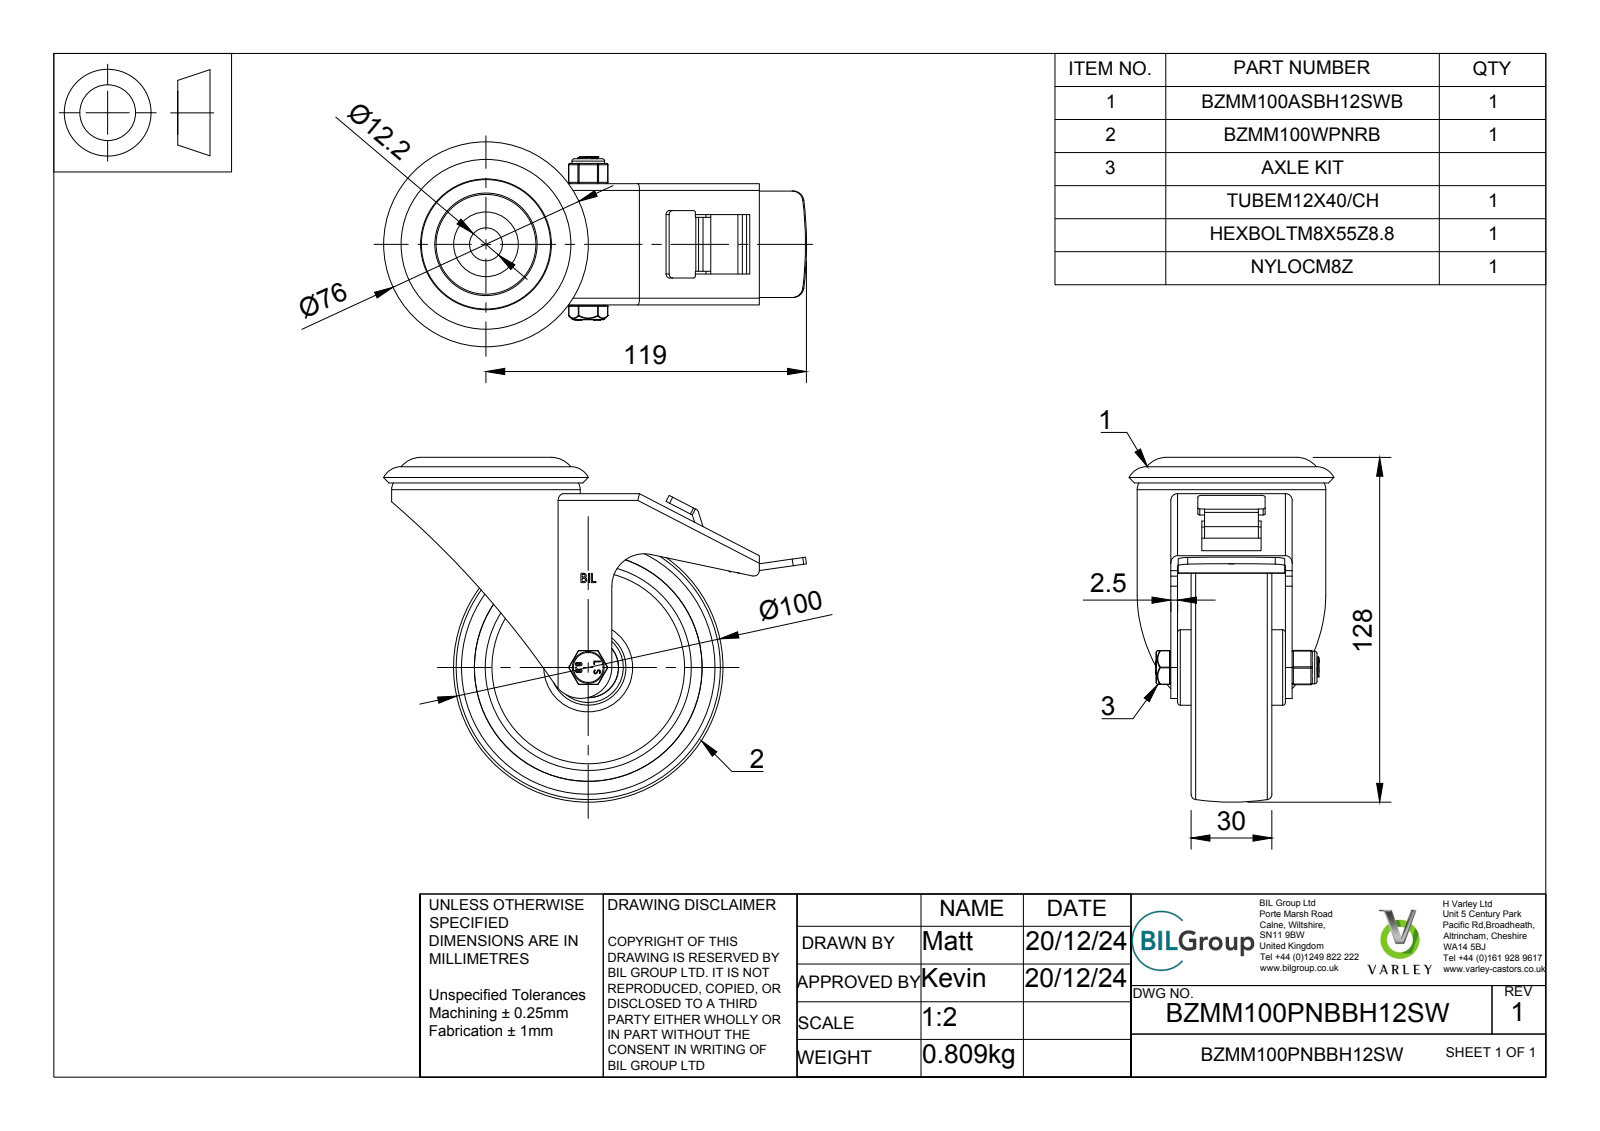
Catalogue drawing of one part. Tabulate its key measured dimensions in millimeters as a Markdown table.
| quantity | value |
| --- | --- |
| part name | BZMM100PNBBH12SW v3; BZMM100ASBH12SWB v1; PRESSED STEEL, ZINC PLATED HEAD; PRESSED STEEL, ZINC PLATED FORKS (+8 more) |
| STEP written by | Autodesk Translation Framework v13.20.0.188 (AP242_MANAGED_MODEL_BASED_3D_ENGINEERING_MIM_LF) |
| units | millimeters |
| bodies | 20 solids, 673 faces (343 planar, 230 cylindrical, 100 other) |
| overall size | 157 × 128 × 76 |
| volume | 206 143 mm³ |
| surface area | 125 605 mm² |
| round holes (diameter × count) | 0.66 × 2, 8 × 1, 8.2 × 1, 8.4 × 1, 8.6 × 1, 12.2 × 1, 12.5 × 1, 13 × 1, 20.5 × 1, 22.5 × 1, 65 × 1, 72 × 1 |
| round bosses / shafts (diameter × count) | 3.9 × 8, 70 × 1, 49.5 × 1, 38 × 1, 28 × 1, 24 × 1, 22.4 × 1, 21.31 × 1 |
| partial cylindrical surfaces (radius × count) | 0.75 × 50, 0.5 × 18, 0.25 × 12, 1.25 × 10, 0.33 × 4, 0.64 × 4, 2.5 × 4, 2 × 3 |
| main face-to-face distances | 2.5, 18, 22, 13, 17, 5, 20.5, 35, 42.5, 37.5 |
| hole center spacings | 3.22, 2.49 |
